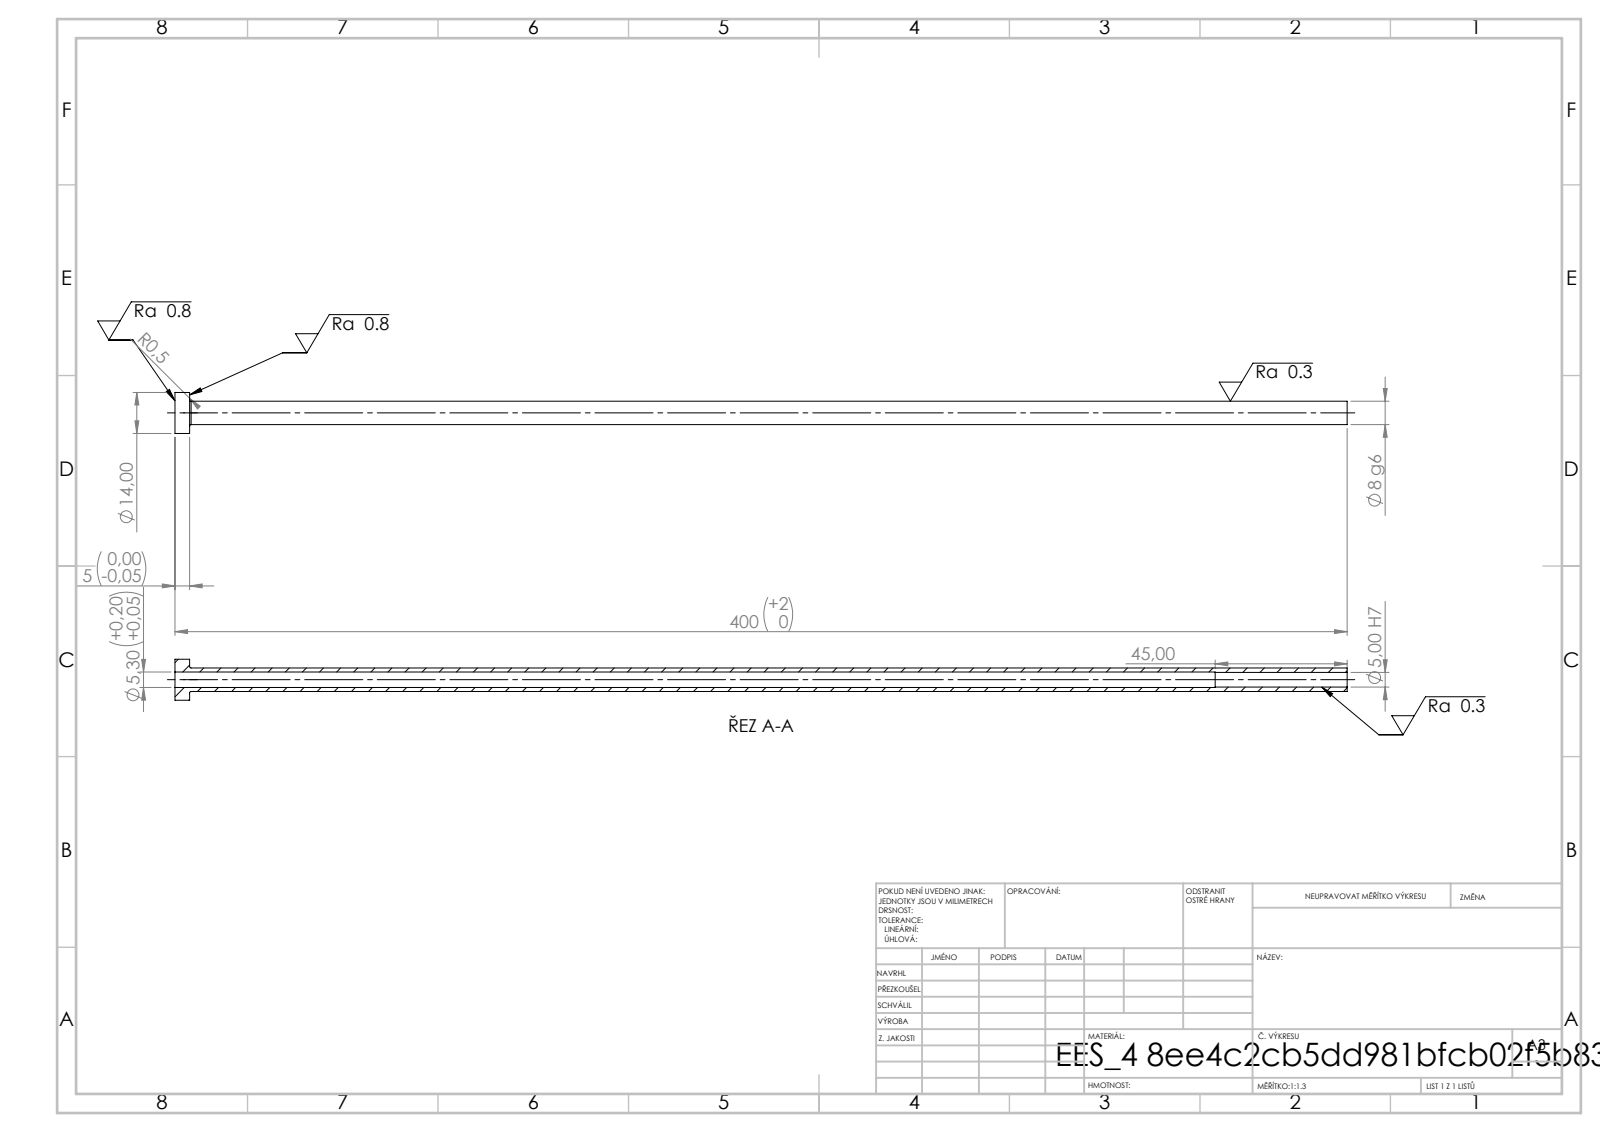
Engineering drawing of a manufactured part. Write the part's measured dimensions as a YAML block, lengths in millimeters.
step_written_by: "SolidWorks 2019 (CONFIG_CONTROL_DESIGN)"
units: millimeters
bodies: {solids: 1, faces: 14, planar: 4, cylindrical: 8, other: 2}
overall_size: [400, 14, 14]
volume: 11910
surface_area: 17028
round_holes:
  - {diameter: 5, count: 1}
  - {diameter: 5.3, count: 1}
round_bosses_or_shafts:
  - {diameter: 14, count: 1}
  - {diameter: 8, count: 1}
face_to_face_distances: [5, 400, 395, 355, 350, 45]
